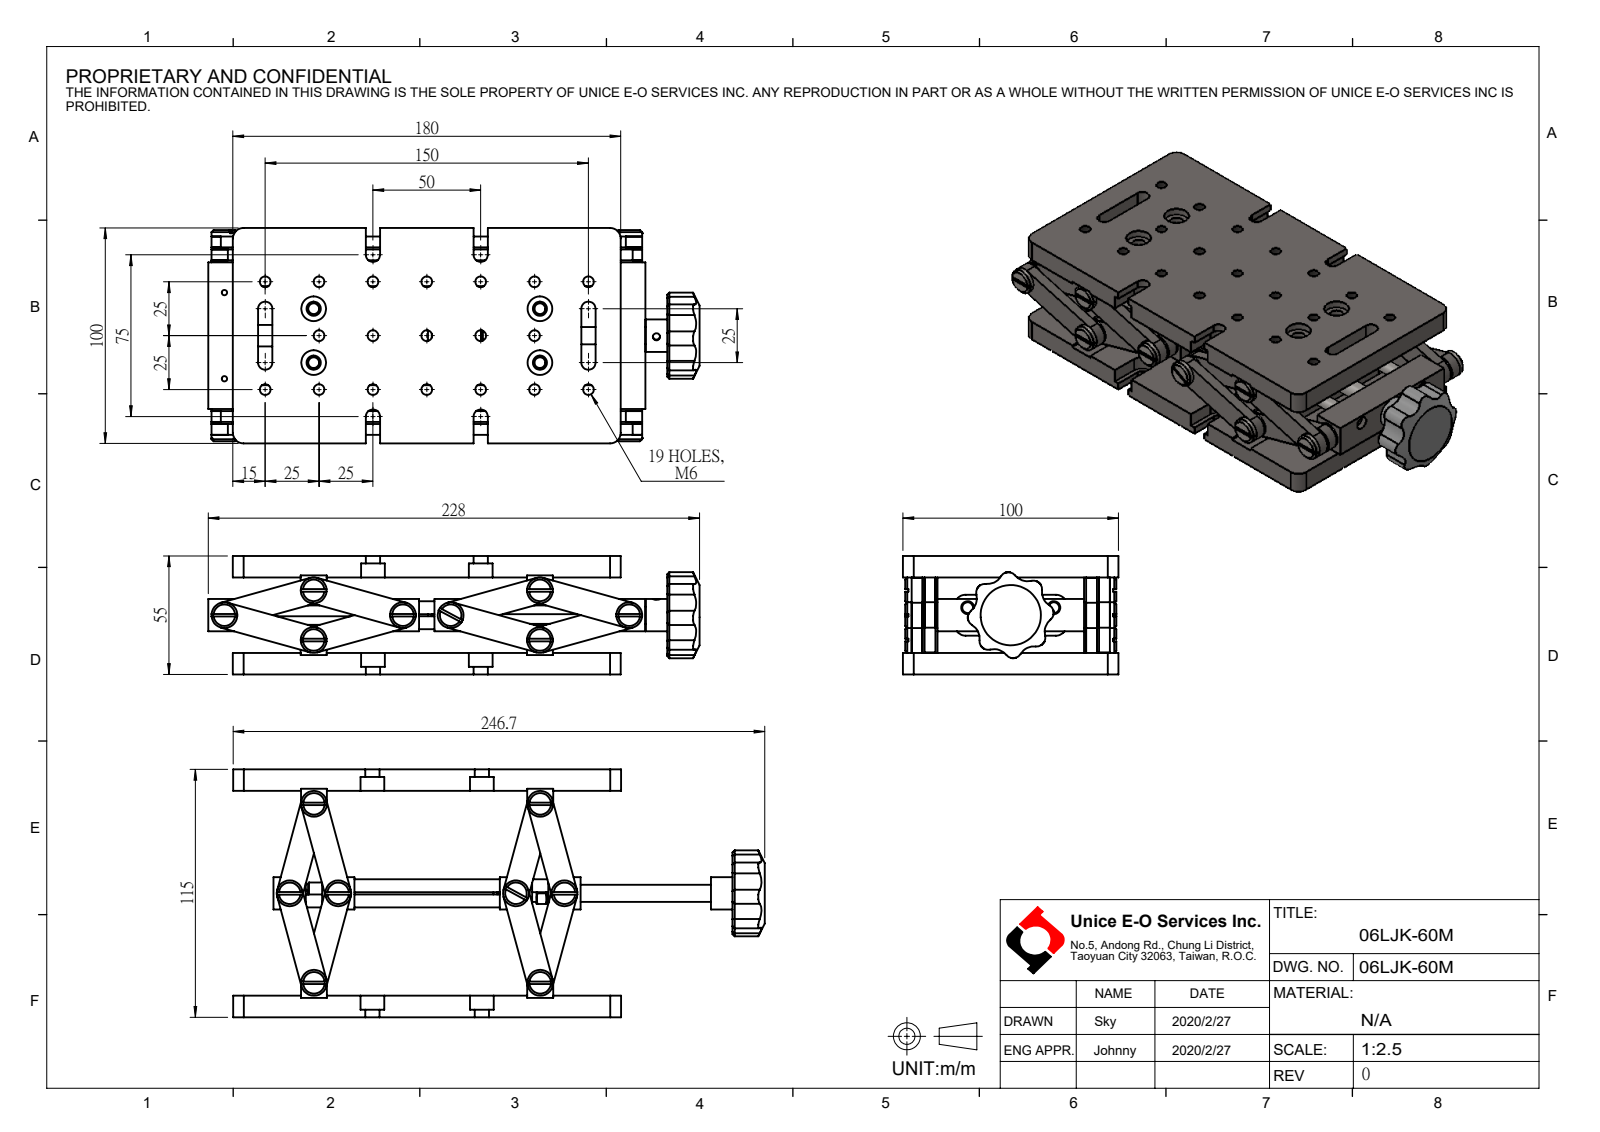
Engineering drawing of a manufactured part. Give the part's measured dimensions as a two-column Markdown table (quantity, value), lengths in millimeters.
| quantity | value |
| --- | --- |
| part name | 06LJK-60M |
| STEP written by | SolidWorks 2016 (CONFIG_CONTROL_DESIGN) |
| units | millimeters |
| bodies | 0 solids, 727 faces (317 planar, 351 cylindrical, 59 other) |
| overall size | 228 × 100 × 55 |
| round holes (diameter × count) | 5 × 19, 2.5 × 4, 6 × 4, 6.6 × 4, 11.5 × 4, 14 × 1 |
| round bosses / shafts (diameter × count) | 12 × 8, 15 × 1, 10 × 1, 8 × 1, 6 × 1 |
| partial cylindrical surfaces (radius × count) | 3.3 × 8, 4 × 8, 7.41 × 8, 5 × 4, 5.5 × 4 |
| main face-to-face distances | 10, 45, 35, 55, 1, 9, 6, 12, 15, 20 |
| hole center spacings | 25, 55.9, 35.36, 50, 79.06, 70.71, 75, 12.75 |
